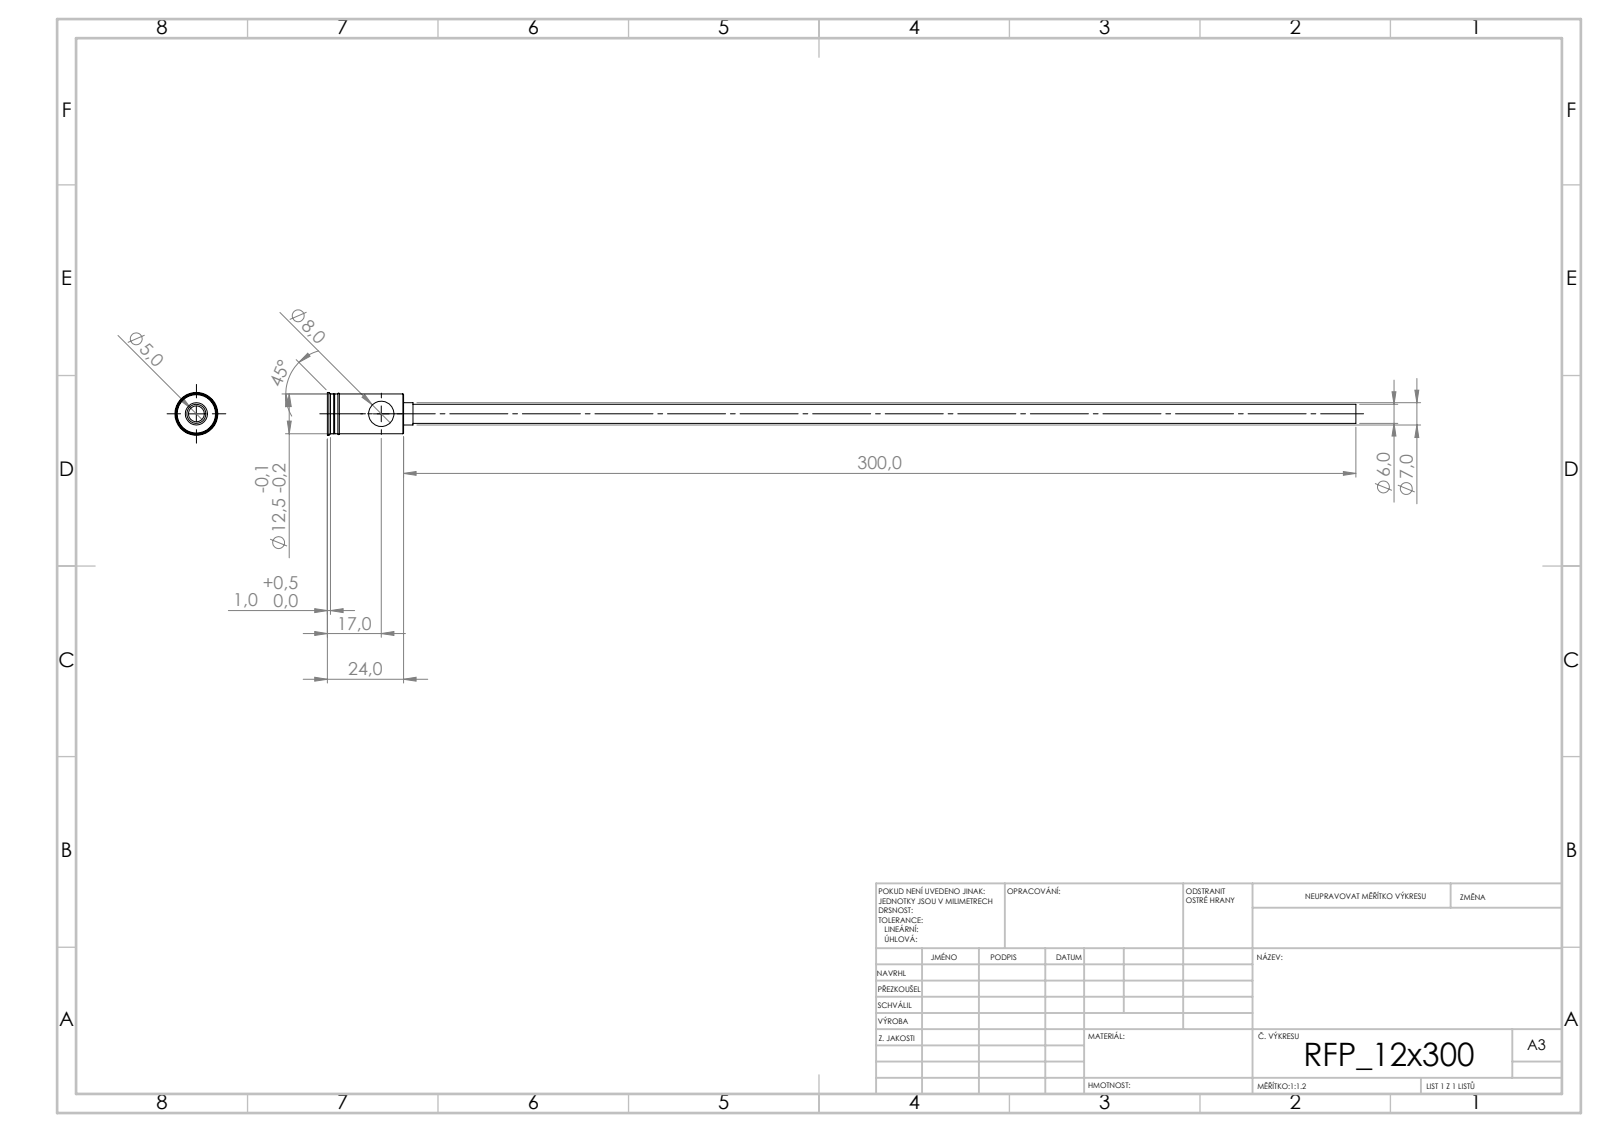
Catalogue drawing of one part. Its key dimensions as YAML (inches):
step_written_by: "SolidWorks 2019 (CONFIG_CONTROL_DESIGN)"
units: inches
bodies: {solids: 1, faces: 44, planar: 20, cylindrical: 16, other: 8}
overall_size: [12.756, 0.531, 0.531]
volume: 0.294
surface_area: 18.38
round_holes:
  - {diameter: 0.197, count: 1}
  - {diameter: 0.315, count: 1}
round_bosses_or_shafts:
  - {diameter: 0.531, count: 1}
  - {diameter: 0.492, count: 1}
  - {diameter: 0.276, count: 1}
  - {diameter: 0.236, count: 1}
face_to_face_distances: [0.945, 0.866, 0.079, 0.311, 0.854, 0.091, 0.118, 0.972, 0.984, 1.063]
